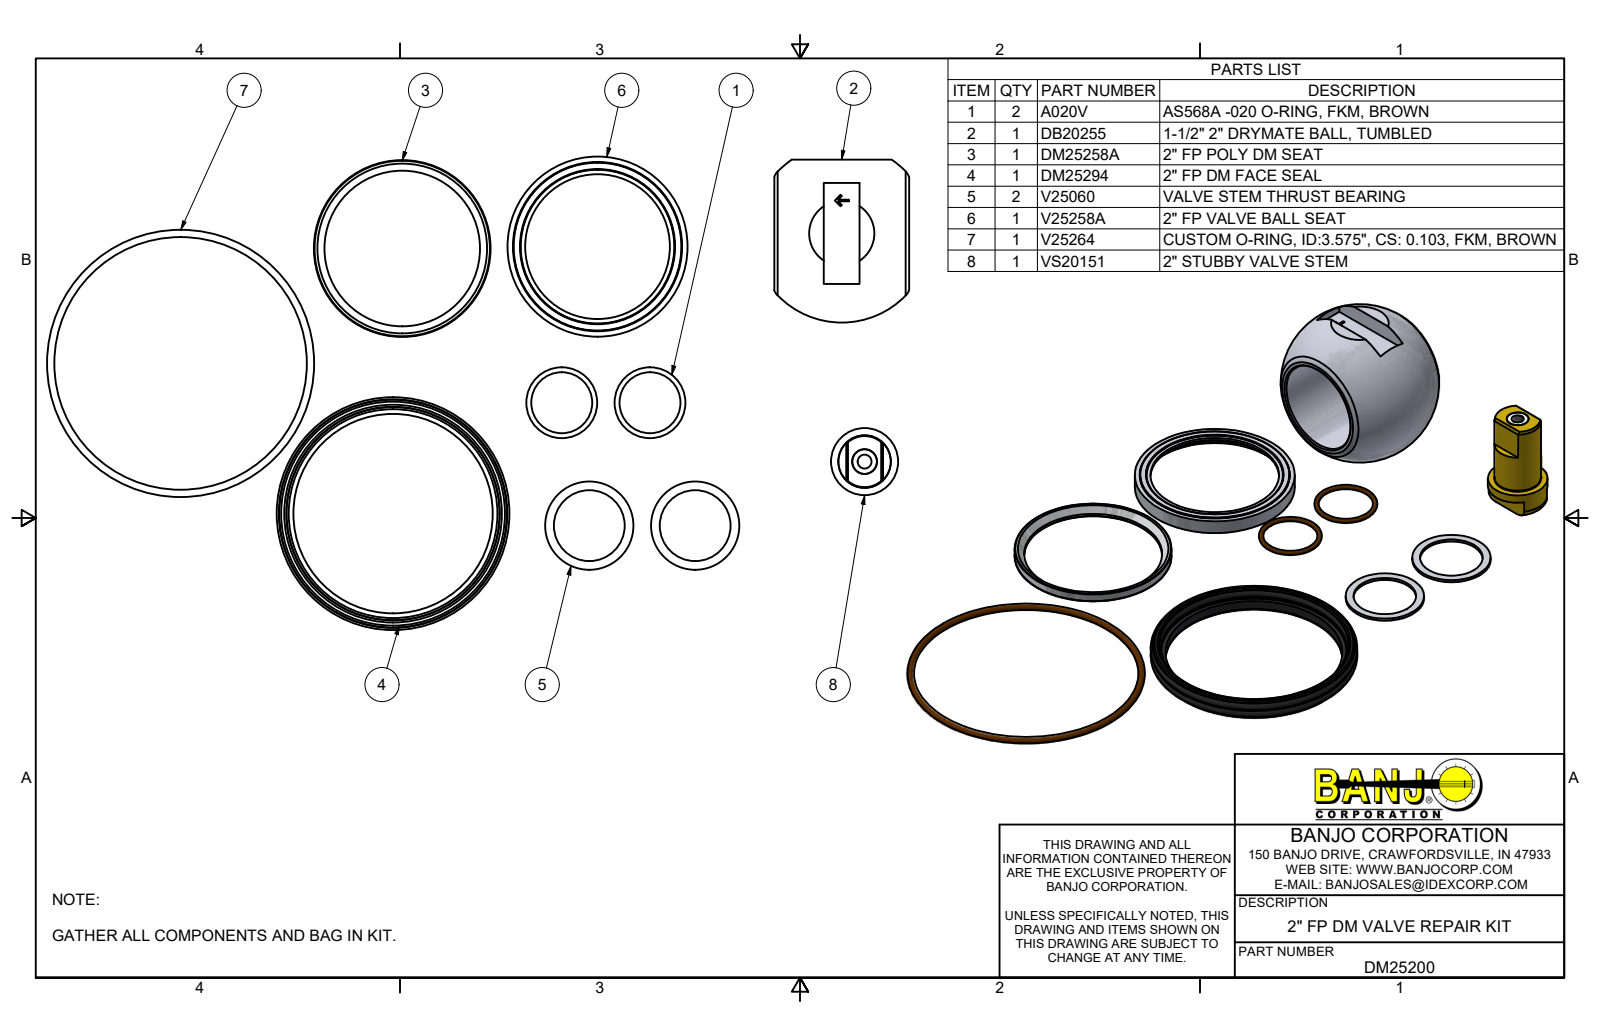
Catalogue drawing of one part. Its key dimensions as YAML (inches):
part_name: "DM25200; A020V; DM25258A; DM25294 (+8 more)"
step_written_by: "Autodesk Inventor 2022 (AUTOMOTIVE_DESIGN)"
units: inches
bodies: {solids: 11, faces: 119, planar: 55, cylindrical: 24, other: 40}
overall_size: [12.209, 6.701, 2.437]
volume: 5.856
surface_area: 61.05
round_holes:
  - {diameter: 1, count: 2}
  - {diameter: 0.196, count: 1}
  - {diameter: 0.351, count: 1}
  - {diameter: 0.375, count: 1}
  - {diameter: 1.455, count: 1}
  - {diameter: 2.05, count: 1}
  - {diameter: 2.185, count: 1}
  - {diameter: 2.2, count: 1}
  - {diameter: 2.235, count: 1}
  - {diameter: 2.82, count: 1}
round_bosses_or_shafts:
  - {diameter: 1.25, count: 2}
  - {diameter: 2.55, count: 1}
  - {diameter: 2.5, count: 1}
  - {diameter: 2.385, count: 1}
  - {diameter: 0.95, count: 1}
  - {diameter: 0.745, count: 1}
face_to_face_distances: [0.325, 0.299, 0.177, 0.188, 0.111, 0.378, 0.365, 0.066, 0.137, 0.026]
hole_center_spacings: [1.5, 2.565, 2.768, 2.784, 3.755, 3.95, 4.004, 4.184]
